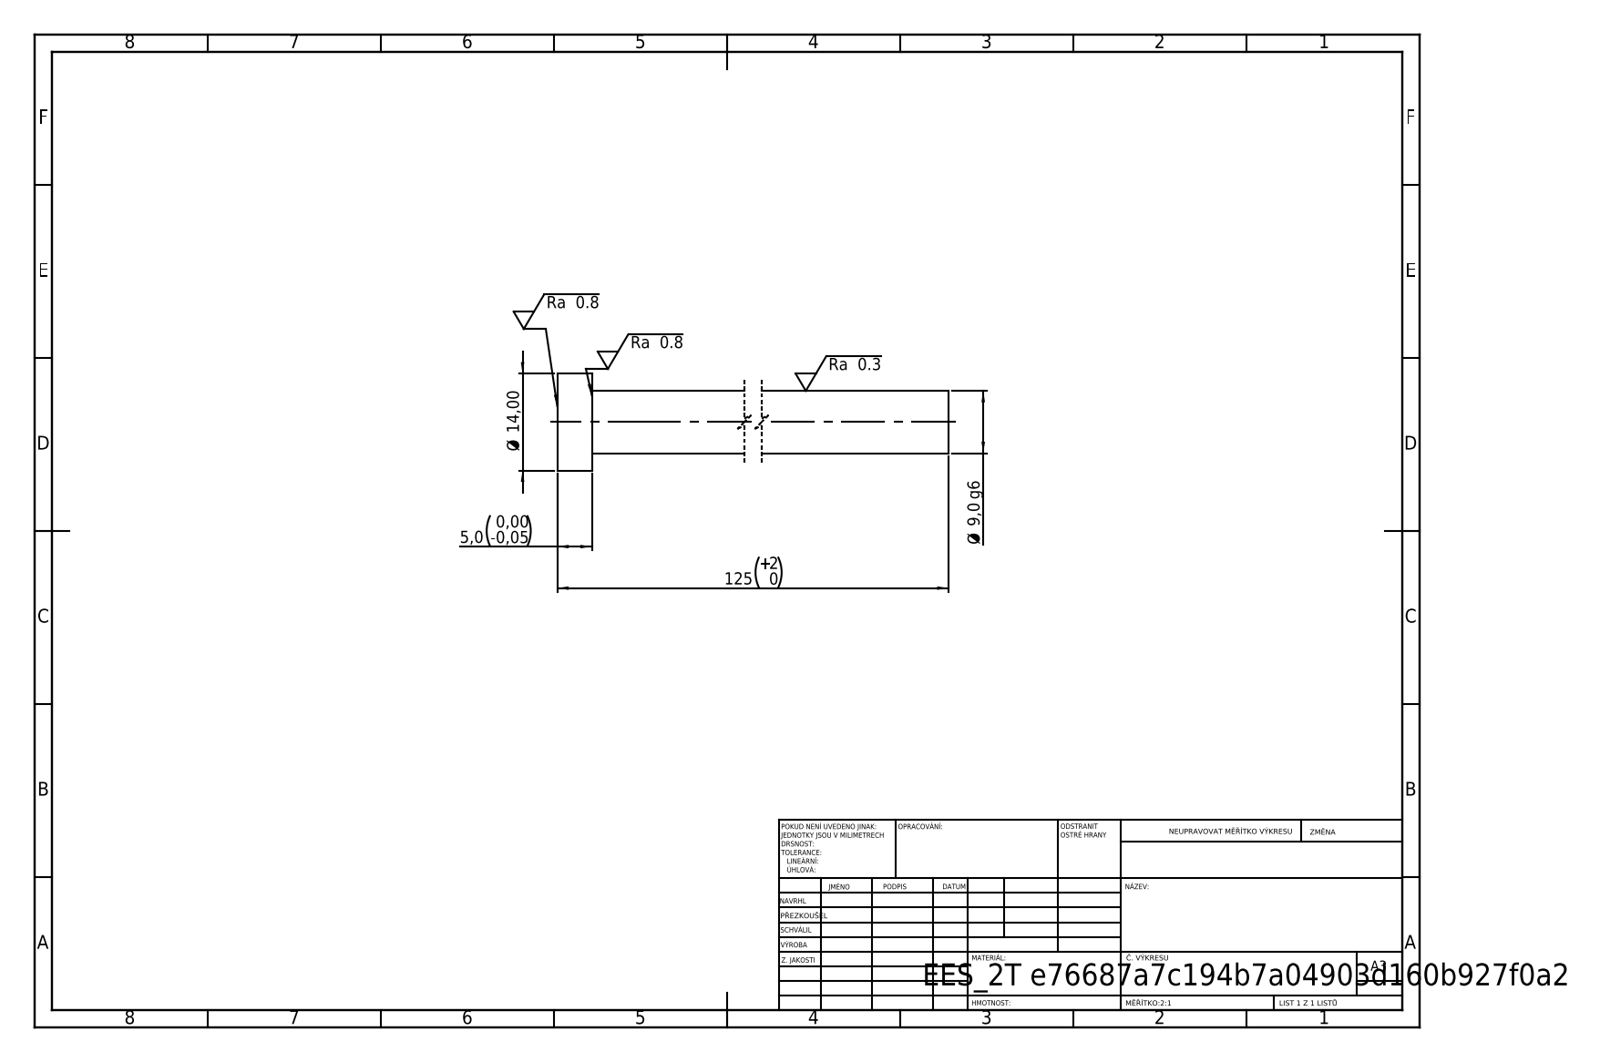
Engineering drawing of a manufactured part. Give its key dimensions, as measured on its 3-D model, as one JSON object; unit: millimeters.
{"step_written_by": "SolidWorks 2019 (CONFIG_CONTROL_DESIGN)", "units": "millimeters", "bodies": {"solids": 1, "faces": 7, "planar": 3, "cylindrical": 4, "other": 0}, "overall_size": [125, 14, 14], "volume_mm3": 8404, "surface_area_mm2": 3921, "round_bosses_or_shafts": [[14, 1], [9, 1]], "face_to_face_distances": [5, 125, 120]}
